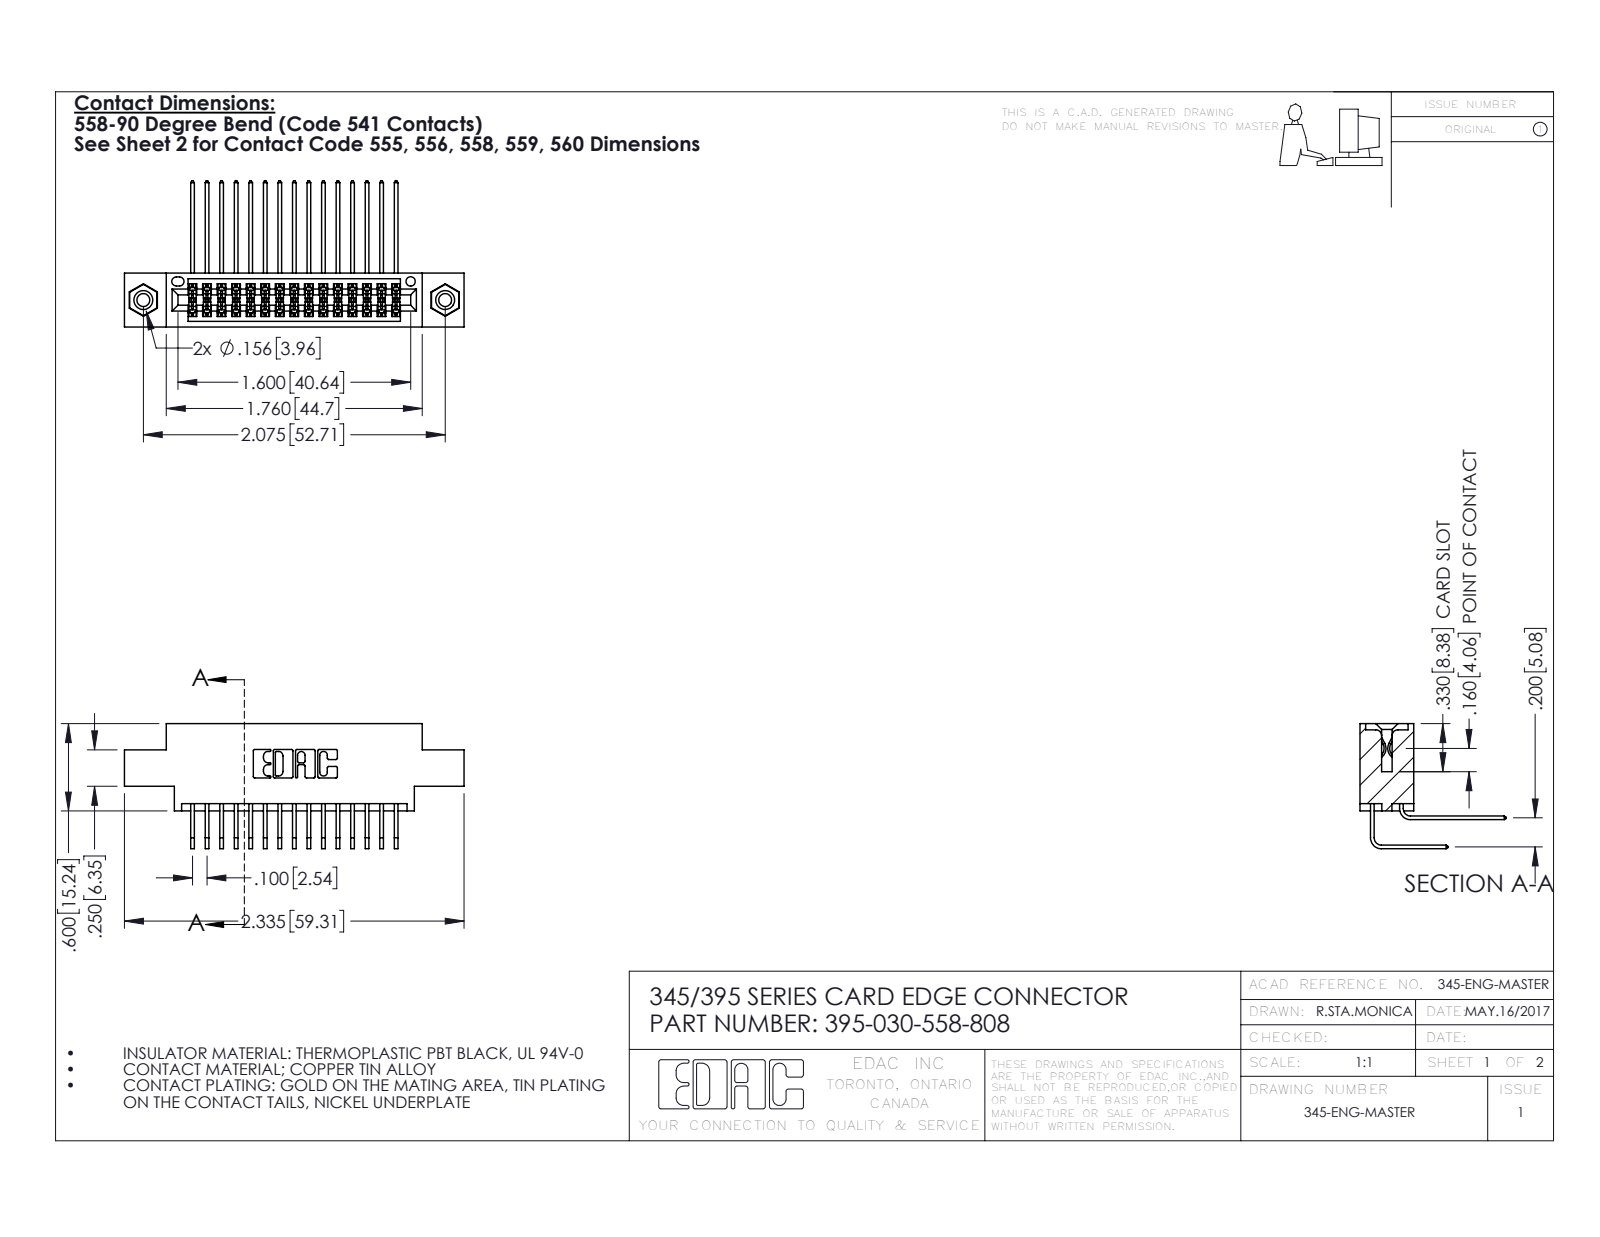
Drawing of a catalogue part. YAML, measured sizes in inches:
part_name: "345-250-001_345-250-003-102; 345-292-001_558 559 Tail - 1; 395-030-558-808; 345-292-001_558 Tail - 2 (+1 more)"
step_written_by: "SolidWorks 2016 (CONFIG_CONTROL_DESIGN)"
units: inches
bodies: {solids: 33, faces: 1750, planar: 1166, cylindrical: 568, other: 16}
overall_size: [2.335, 1.005, 0.859]
volume: 0.34
surface_area: 13.44
round_holes:
  - {diameter: 0.089, count: 2}
  - {diameter: 0.125, count: 2}
  - {diameter: 0.156, count: 2}
  - {diameter: 0.064, count: 1}
round_bosses_or_shafts:
  - {diameter: 0.155, count: 2}
partial_cylinders:
  - {radius: 0.006, count: 46}
  - {radius: 0.01, count: 22}
  - {radius: 0.007, count: 6}
  - {radius: 0.031, count: 6}
  - {radius: 0.026, count: 3}
  - {radius: 0.014, count: 2}
  - {radius: 0.019, count: 2}
  - {radius: 0.022, count: 2}
face_to_face_distances: [0.2, 0.072, 0.298, 0.37, 0.098, 0.272, 0.025, 0.225, 0.1, 0.175]
hole_center_spacings: [0.27, 1.842, 2.075]
